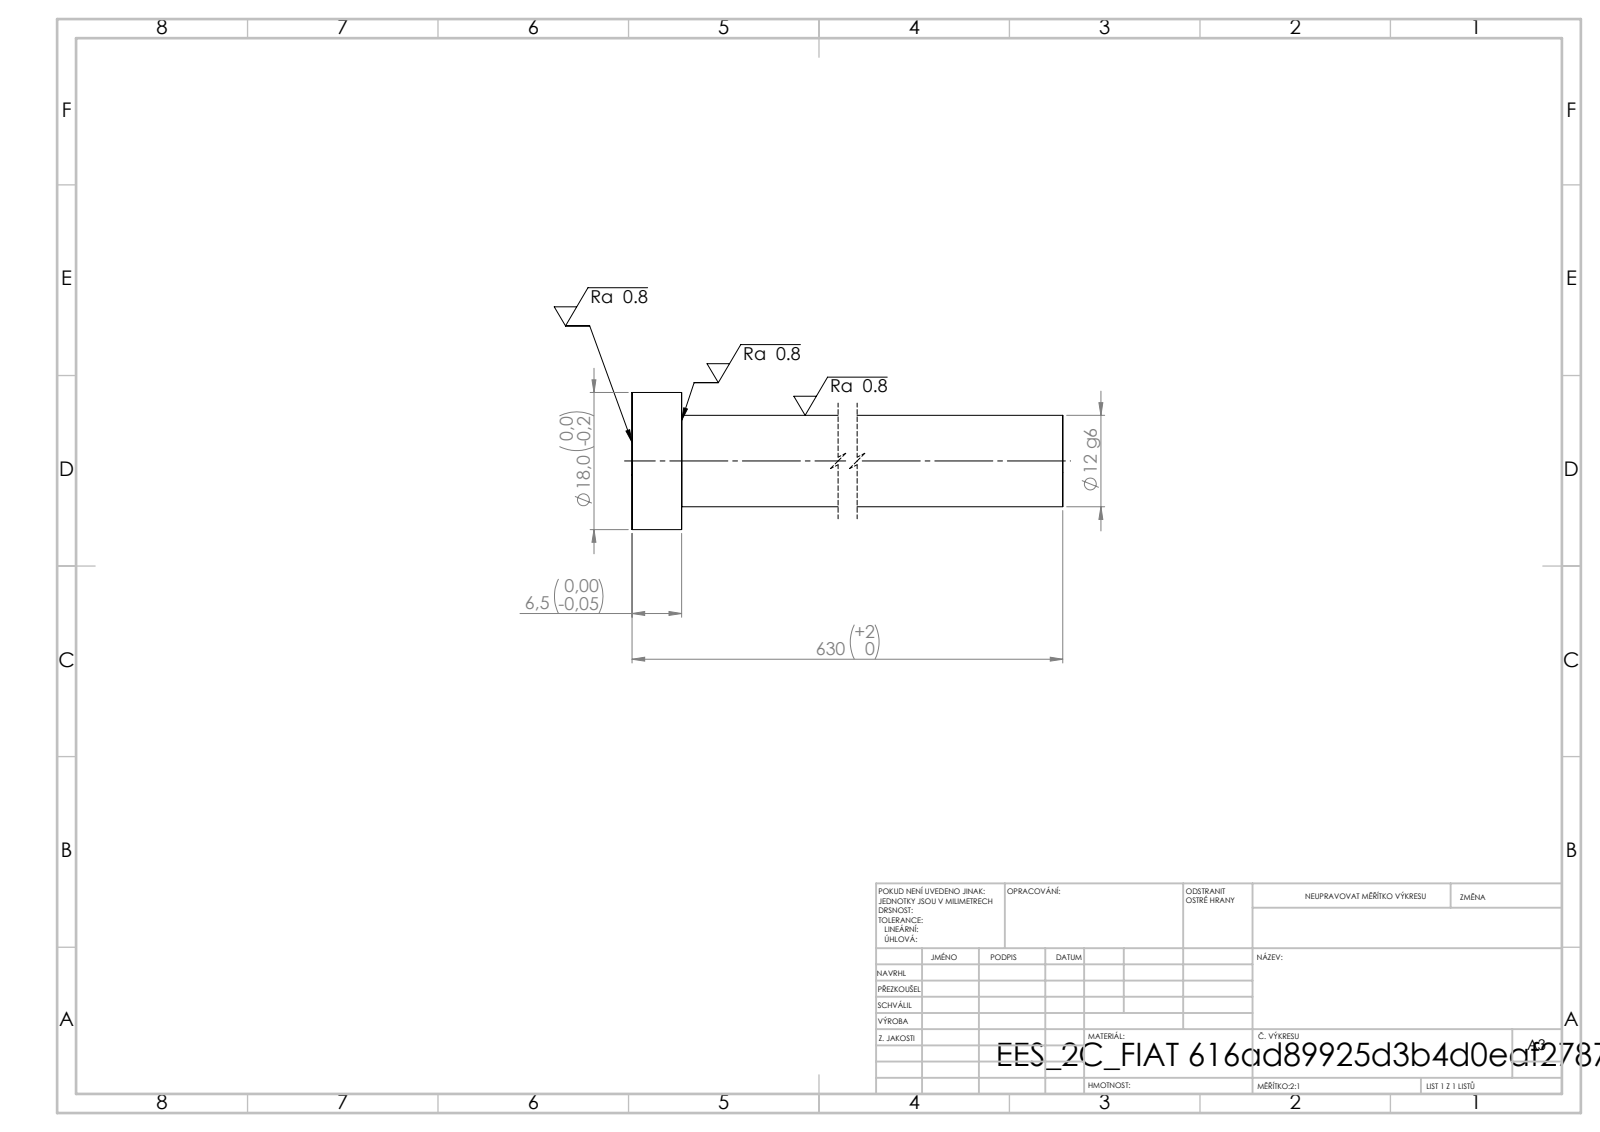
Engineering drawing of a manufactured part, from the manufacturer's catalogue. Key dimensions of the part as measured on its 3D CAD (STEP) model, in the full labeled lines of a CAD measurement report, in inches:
STEP written by: SolidWorks 2019 (CONFIG_CONTROL_DESIGN)
Units: inches
Bodies: 1 solid, 7 faces (3 planar, 4 cylindrical, 0 other)
Overall size (bounding box): 24.803 × 0.709 × 0.709
Volume: 4.404 in³ · Surface area: 37.79 in²
Round bosses / shafts (diameter × count): ⌀0.709 ×1, ⌀0.472 ×1
Main face-to-face distances: 0.256, 24.803, 24.547
